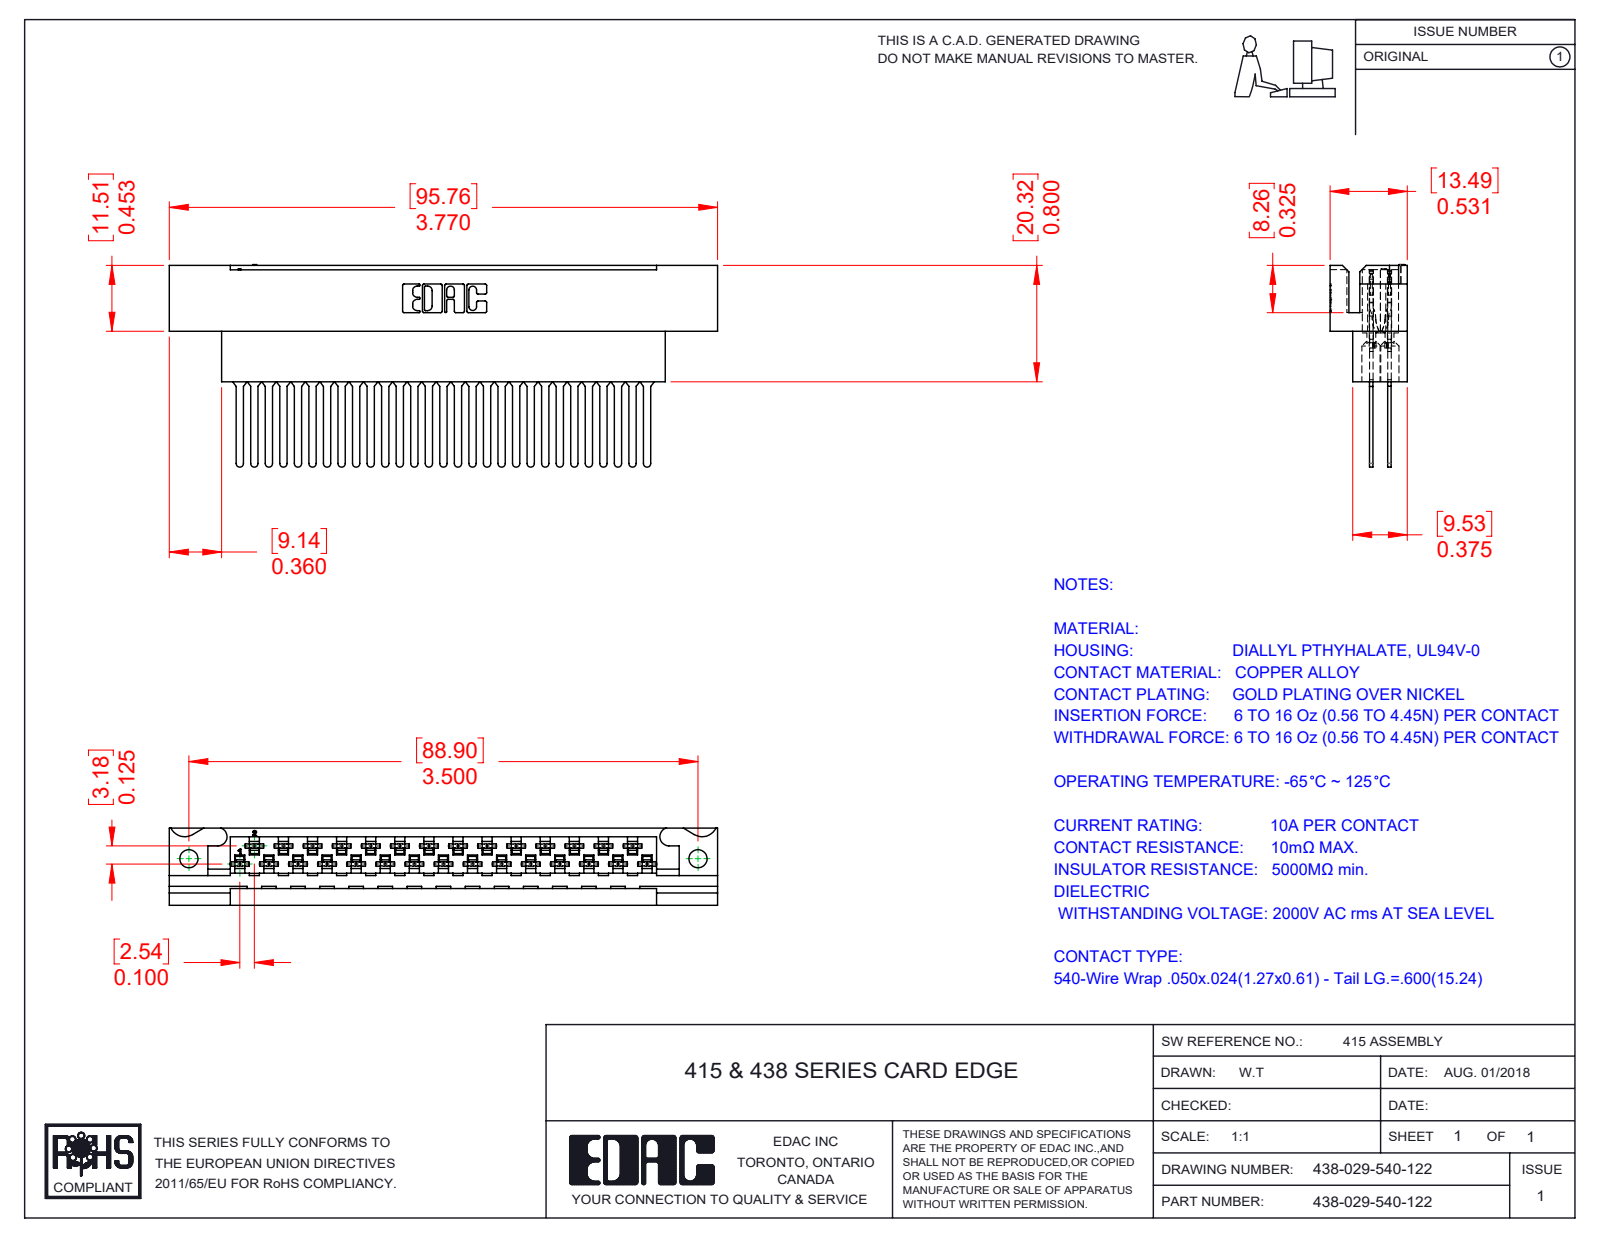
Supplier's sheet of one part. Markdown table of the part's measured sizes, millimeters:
| quantity | value |
| --- | --- |
| part name | 438-029-540-122; 438-210-001_438-210-029-112; 516-290-001_540 |
| STEP written by | SolidWorks 2016 (CONFIG_CONTROL_DESIGN) |
| units | millimeters |
| bodies | 30 solids, 2998 faces (1911 planar, 804 cylindrical, 283 other) |
| overall size | 95.76 × 35.34 × 13.49 |
| volume | 15 786 mm³ |
| surface area | 20 234 mm² |
| round holes (diameter × count) | 1.27 × 29, 3.3 × 29, 3.17 × 1, 3.18 × 1 |
| partial cylindrical surfaces (radius × count) | 0.3 × 116, 0.56 × 116, 0.18 × 58, 0.2 × 58, 0.41 × 58, 2.03 × 58, 0.64 × 29, 0.25 × 22 |
| main face-to-face distances | 3.18, 0.61, 1.88, 1.27, 7.49, 13.49, 2.92, 3.96, 6.61, 6.88 |
| hole center spacings | 5.08, 10.16, 15.24, 20.32, 25.4, 30.48, 35.56, 2.54 |
